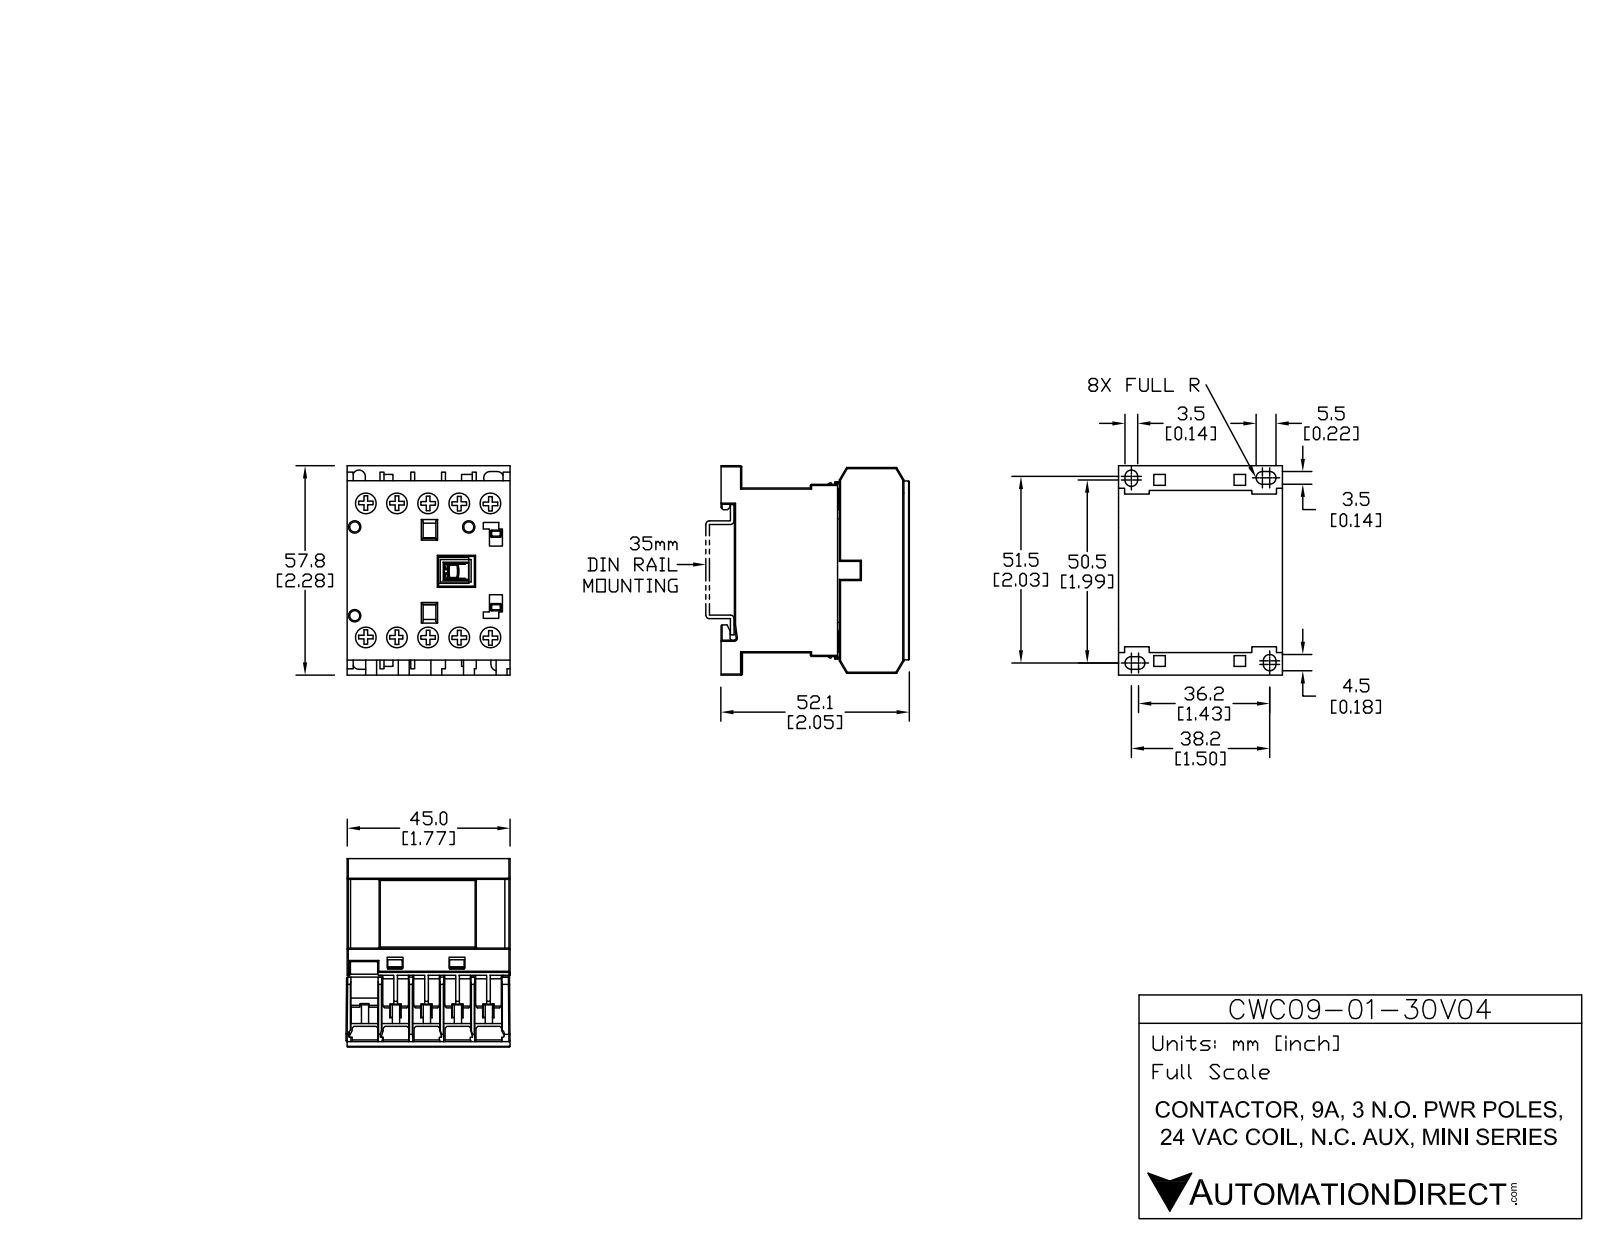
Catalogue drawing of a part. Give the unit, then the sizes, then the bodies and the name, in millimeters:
Units: millimetres
Overall size (bounding box): 58.04 × 52.12 × 45.75
Round holes (diameter × count): ⌀6.2 ×10, ⌀2.8 ×3
Round bosses / shafts (diameter × count): ⌀5.9 ×10
Partial cylindrical surfaces — rounded edges, fillets, slot ends (radius × count): R0.3 ×20, R1.72 ×6, R1.73 ×2, R0.32 ×1, R0.42 ×1, R0.55 ×1
Main face-to-face distances: 8.25, 45.5, 1.25, 16.5, 9.5, 5.5, 17.75, 5.13, 10.63, 7
Hole centre spacings: 8.55, 37.94, 17.1, 40.72, 36.96, 25.65, 44.99, 6.91
Volume: 97 133 mm³ · Surface area: 30 437 mm²
Bodies: 15 solids, 535 faces (445 planar, 90 cylindrical, 0 other)
Part name (STEP PRODUCT): CWC09-01-30V04
STEP written by: SolidWorks 2013 (AUTOMOTIVE_DESIGN)
